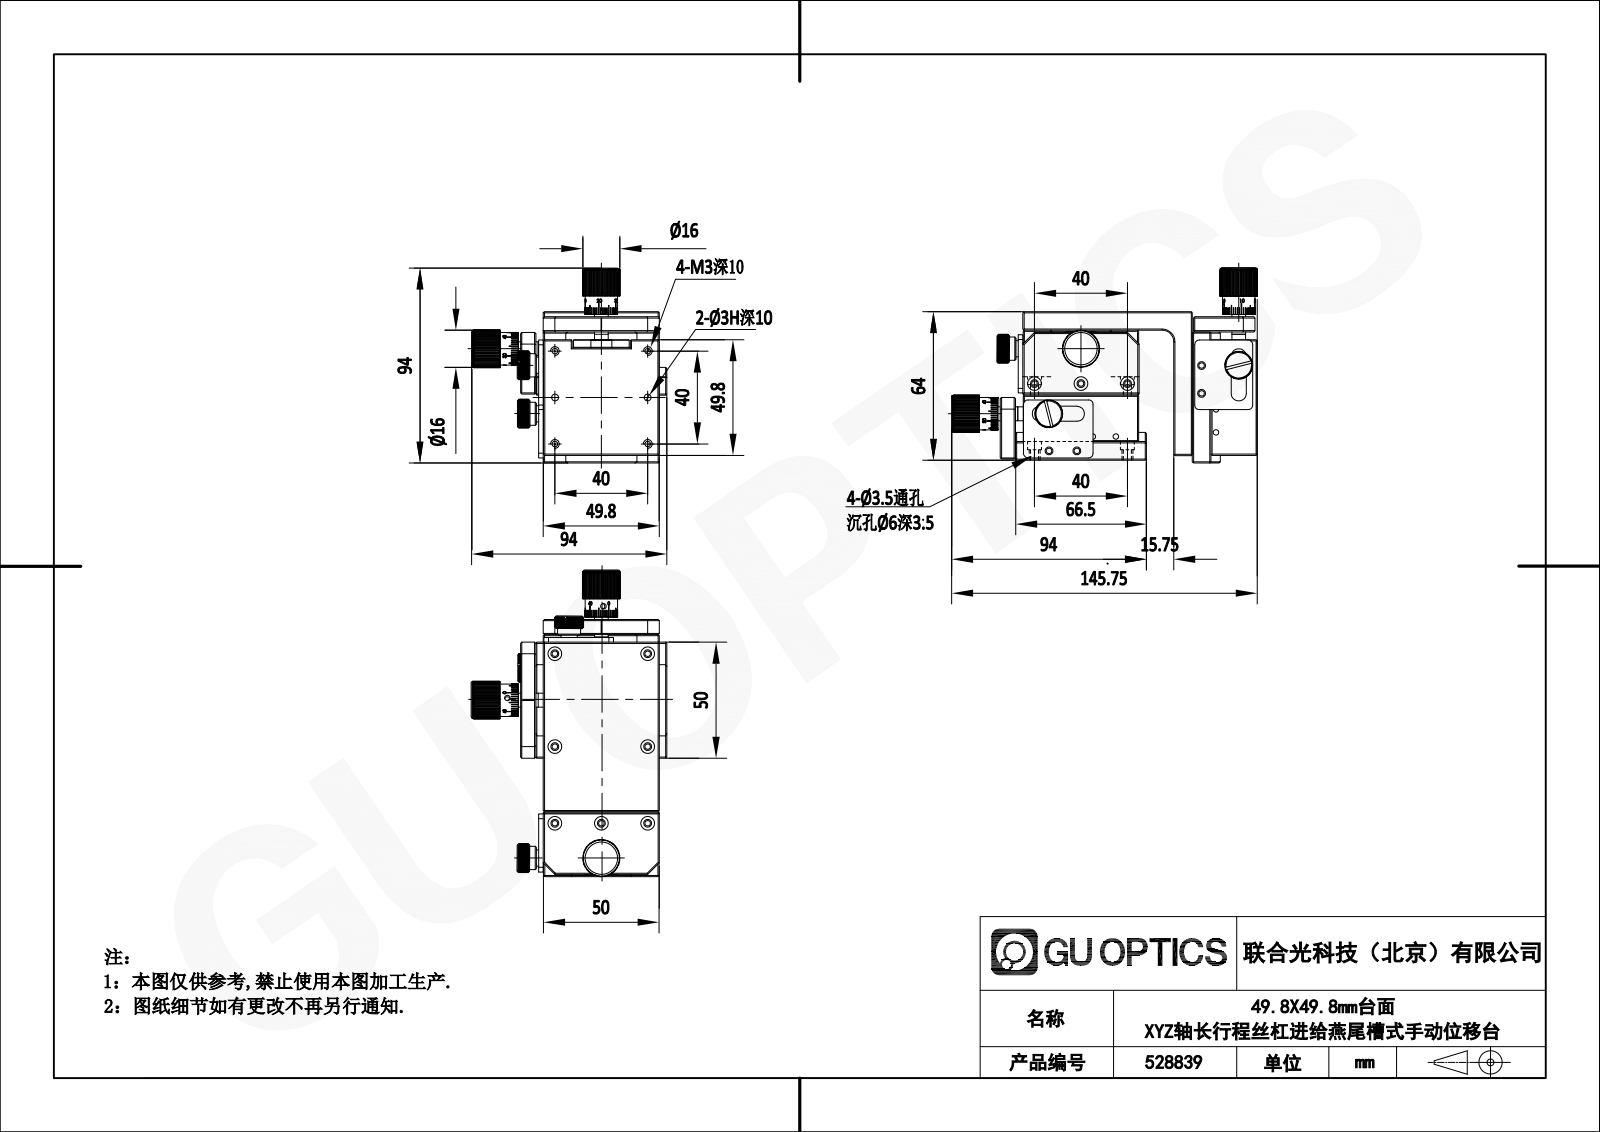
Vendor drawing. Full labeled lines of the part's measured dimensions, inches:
Part name (STEP PRODUCT): 528839
STEP written by: SolidWorks 2020 (CONFIG_CONTROL_DESIGN)
Units: inches
Bodies: 0 solids, 2158 faces (1085 planar, 533 cylindrical, 540 other)
Overall size (bounding box): 6.683 × 3.748 × 3.701
Round holes (diameter × count): ⌀0.098 ×35, ⌀0.081 ×18, ⌀0.134 ×17, ⌀0.236 ×16, ⌀0.114 ×12, ⌀0.197 ×12, ⌀0.118 ×11, ⌀0.13 ×9, ⌀0.256 ×8, ⌀0.059 ×6, ⌀0.122 ×6, ⌀0.138 ×3
Round bosses / shafts (diameter × count): ⌀0.118 ×18, ⌀0.177 ×12, ⌀0.098 ×12, ⌀0.217 ×10, ⌀0.22 ×6, ⌀0.512 ×3, ⌀0.472 ×3, ⌀0.406 ×3
Partial cylindrical surfaces — rounded edges, fillets, slot ends (radius × count): R0.012 ×24, R0.079 ×12, R0.083 ×6, R0.295 ×3, R0.453 ×3
Main face-to-face distances: 1.102, 0.472, 0.63, 1.094, 0.315, 0.177, 0.807, 0.287, 0.465, 0.295
Hole centre spacings: 0.335, 0.787, 1.761, 1.575, 0.591, 1.113, 0.535, 0.58
